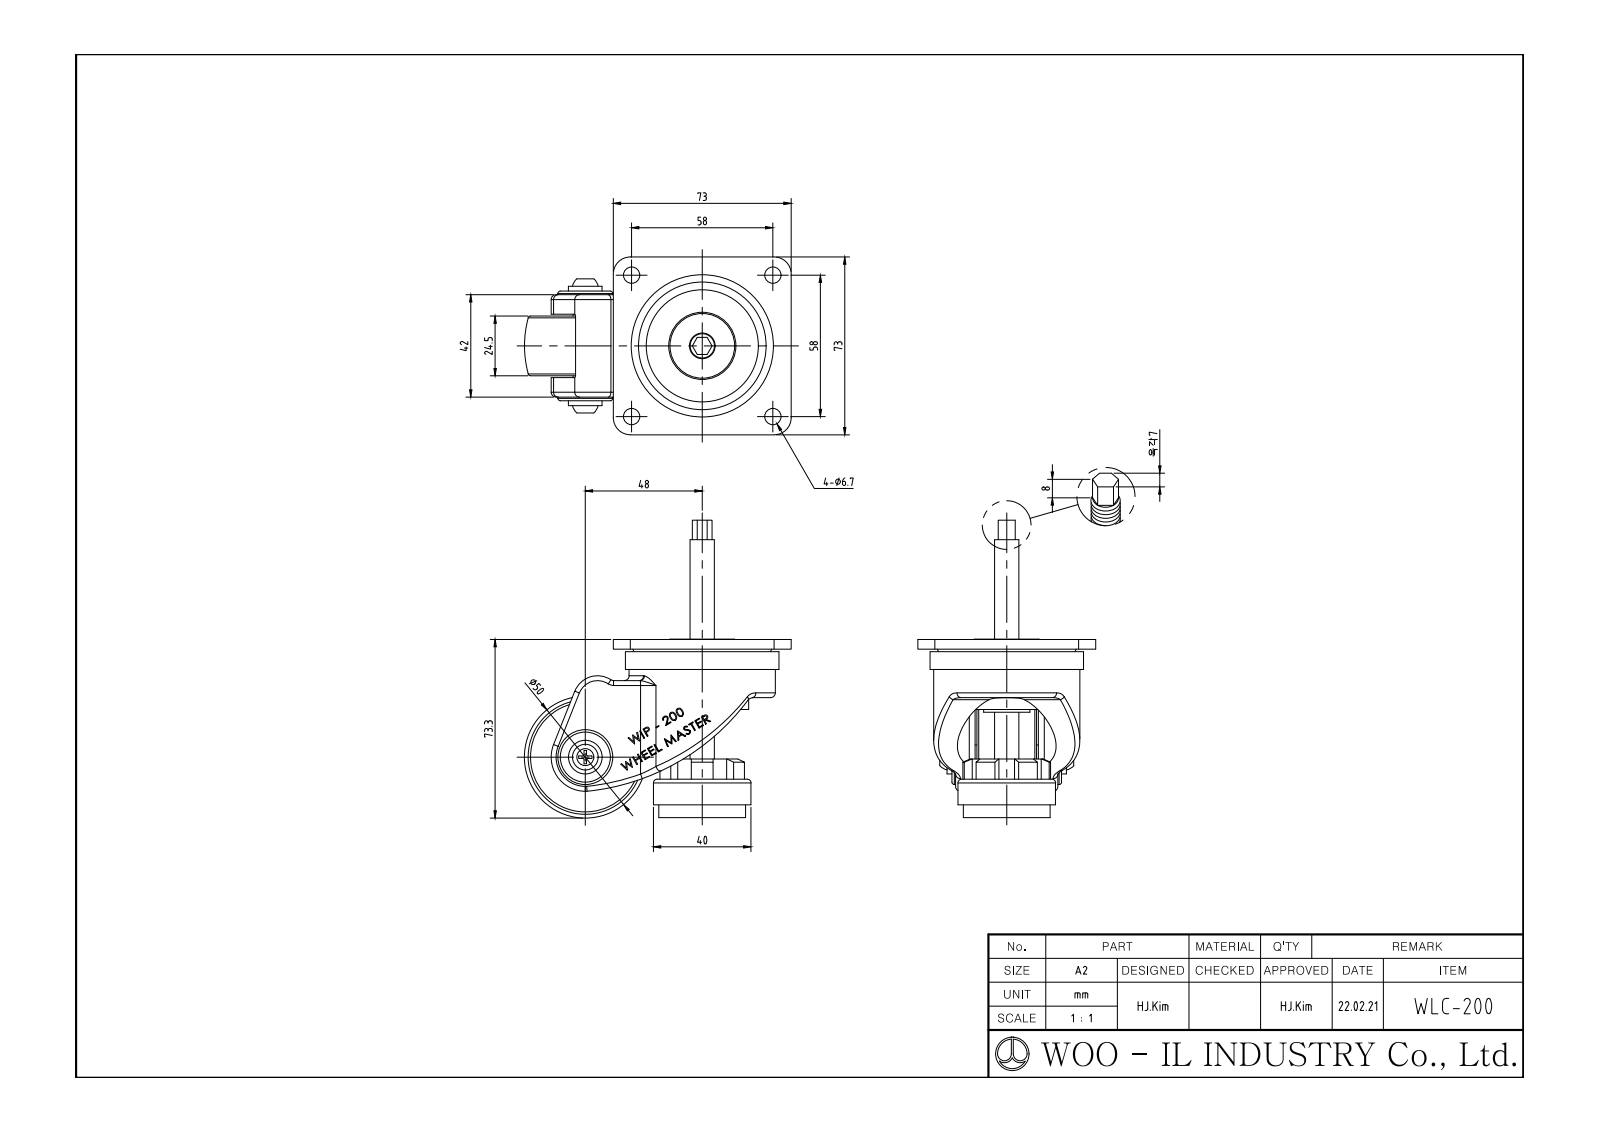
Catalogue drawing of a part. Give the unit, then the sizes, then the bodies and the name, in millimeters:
Units: millimetres
Overall size (bounding box): 122.24 × 109.5 × 73
Round bosses / shafts (diameter × count): ⌀51.19 ×1, ⌀26.45 ×1
Main face-to-face distances: 28.91, 6.5, 22.41
Volume: 201 239 mm³ · Surface area: 51 338 mm²
Bodies: 1 solid, 686 faces (3 planar, 6 cylindrical, 677 other)
Part name (STEP PRODUCT): WLC-200F
STEP written by: SolidWorks 2019 (AUTOMOTIVE_DESIGN)
